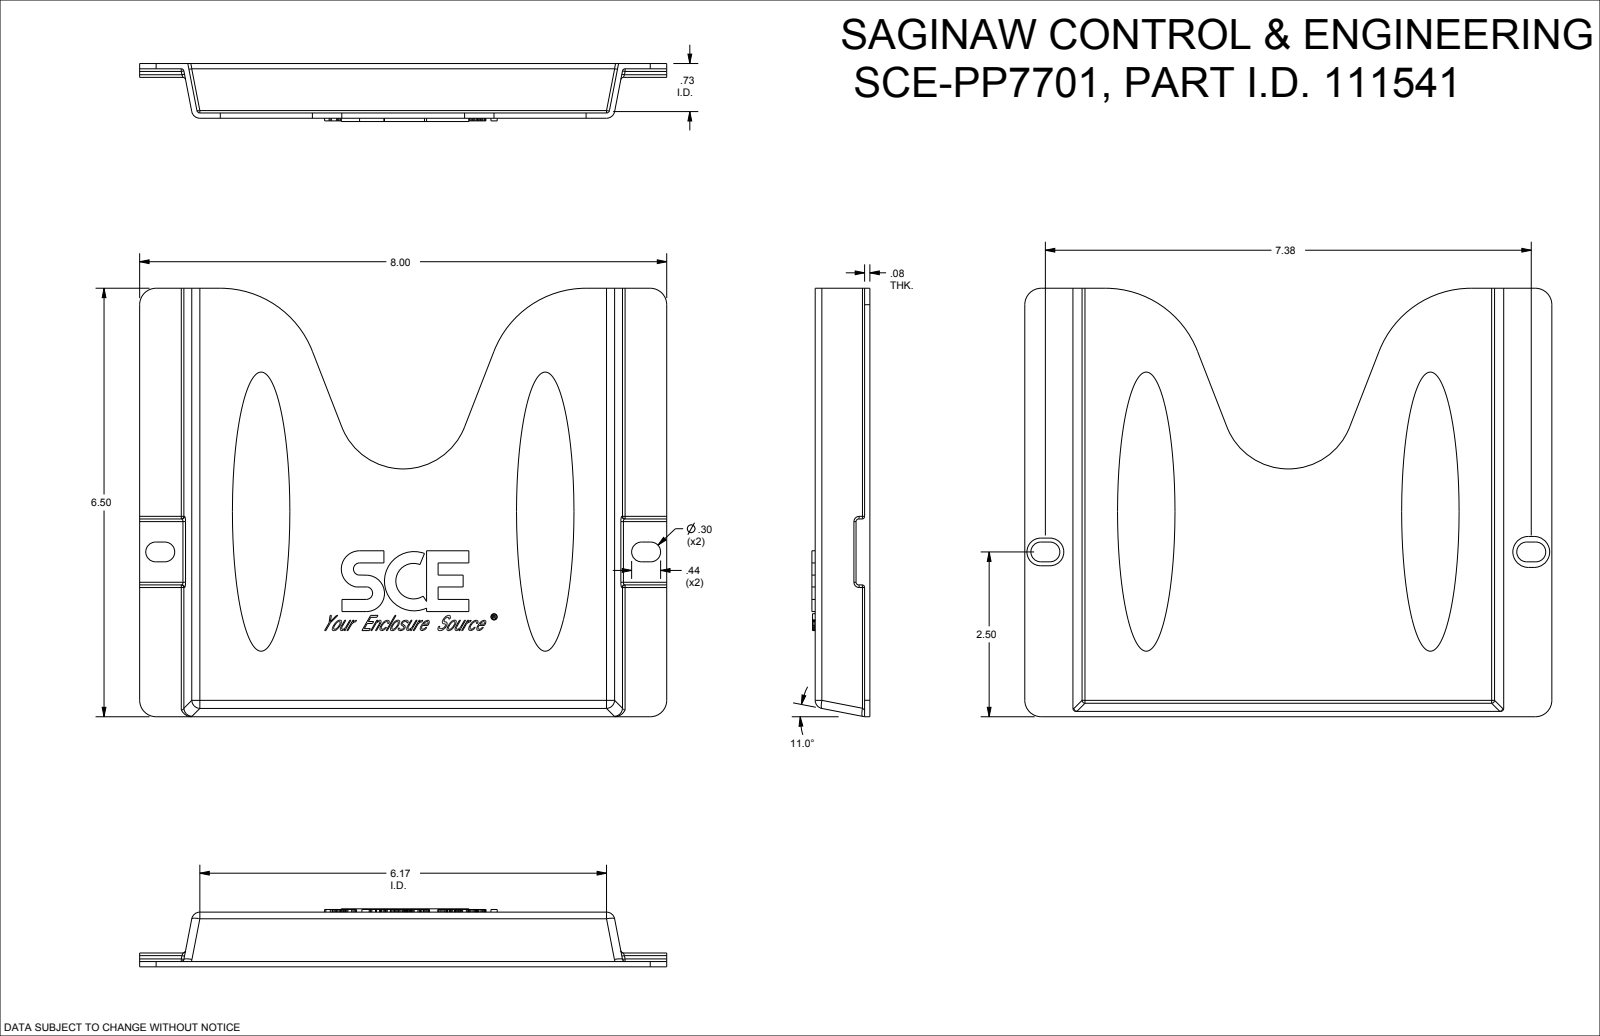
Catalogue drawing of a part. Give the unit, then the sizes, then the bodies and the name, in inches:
Units: inches
Overall size (bounding box): 8 × 6.5 × 0.88
Round holes (diameter × count): ⌀0.086 ×1
Round bosses / shafts (diameter × count): ⌀0.095 ×1
Partial cylindrical surfaces — rounded edges, fillets, slot ends (radius × count): R0.04 ×12, R0.045 ×7, R0.125 ×5, R0.15 ×4, R0.21 ×4, R0.25 ×4, R0.235 ×2, R1.5 ×2
Main face-to-face distances: 0.08, 0.75, 0.83, 0.67, 0.08, 0.13, 0.05, 0.88, 0.8, 0.54
Volume: 4.224 in³ · Surface area: 107 in²
Bodies: 1 solid, 759 faces (678 planar, 59 cylindrical, 22 other)
Part name (STEP PRODUCT): SCE-PP7701
STEP written by: SolidWorks 2021 (AUTOMOTIVE_DESIGN)
